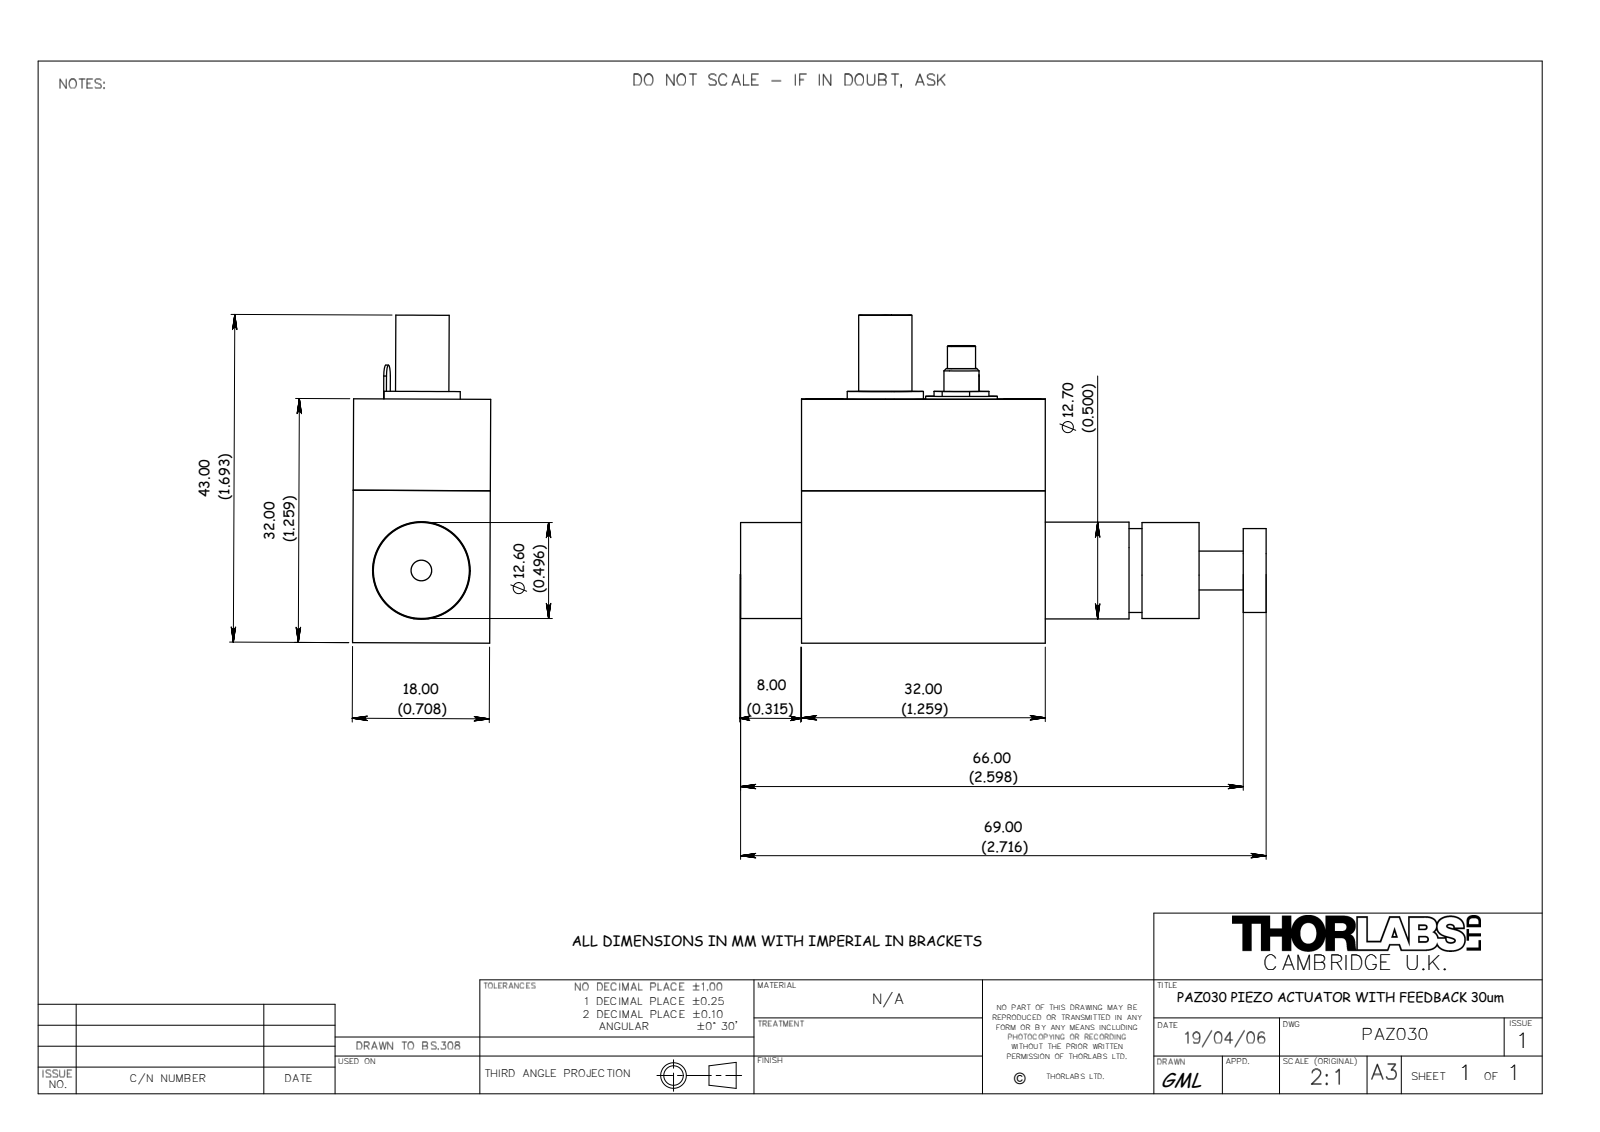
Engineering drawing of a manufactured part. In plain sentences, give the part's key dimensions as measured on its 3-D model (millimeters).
The part is named "15664-E0W". Its 3-D file was written by "SolidWorks 2007 (AUTOMOTIVE_DESIGN)". It is 0 solids with 133 faces: 66 planar, 51 cylindrical and 16 other. Overall it measures 69 by 44.44 by 22.88 millimeters. Round holes: 2 of diameter 2.5, 2 of diameter 5, 1 of diameter 2.71, 1 of diameter 3, 1 of diameter 5.1, 1 of diameter 5.3, 1 of diameter 11.4, 1 of diameter 12.8. Round bosses or shafts: 1 of diameter 12.7, 1 of diameter 12.6, 1 of diameter 11, 1 of diameter 10, 1 of diameter 9.4, 1 of diameter 9, 1 of diameter 7, 1 of diameter 5.1. Partial cylindrical surfaces (rounded edges, fillets, slot ends): 2 of radius 1.5, 1 of radius 1.44, 1 of radius 2. The main face-to-face distances are 18, 31.99, 32, 1, 17, 8, 40, 20.2, 52.2, 60.2. The hole center spacings are 26, 8, 18.
